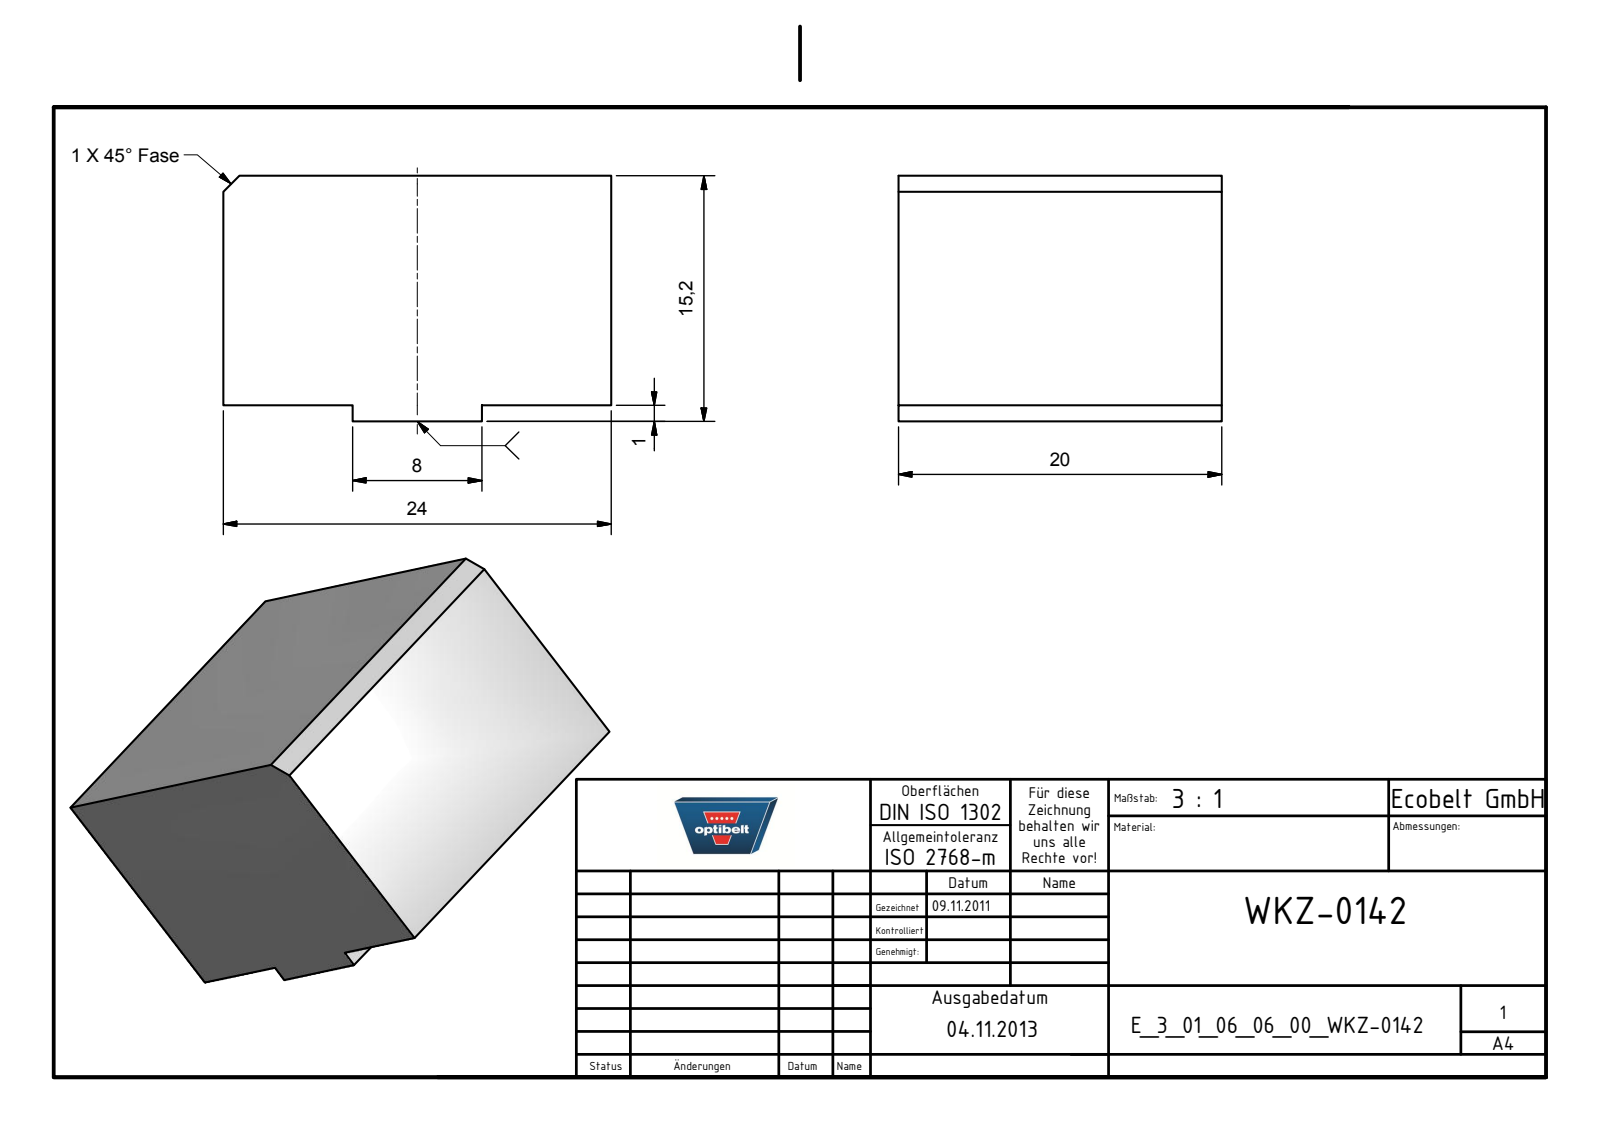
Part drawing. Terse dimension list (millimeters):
name: E_3_01_06_06_00_WKZ-0142
written by: Autodesk Inventor 2025 (AUTOMOTIVE_DESIGN)
unit: mm
bodies: 1 solid, 11 faces (11 planar, 0 cylindrical, 0 other)
size: 24 × 20 × 15.2
volume: 6 966 mm³; area: 2 253 mm²
face distances: 20, 14.2, 24, 1, 15.2, 8, 16
